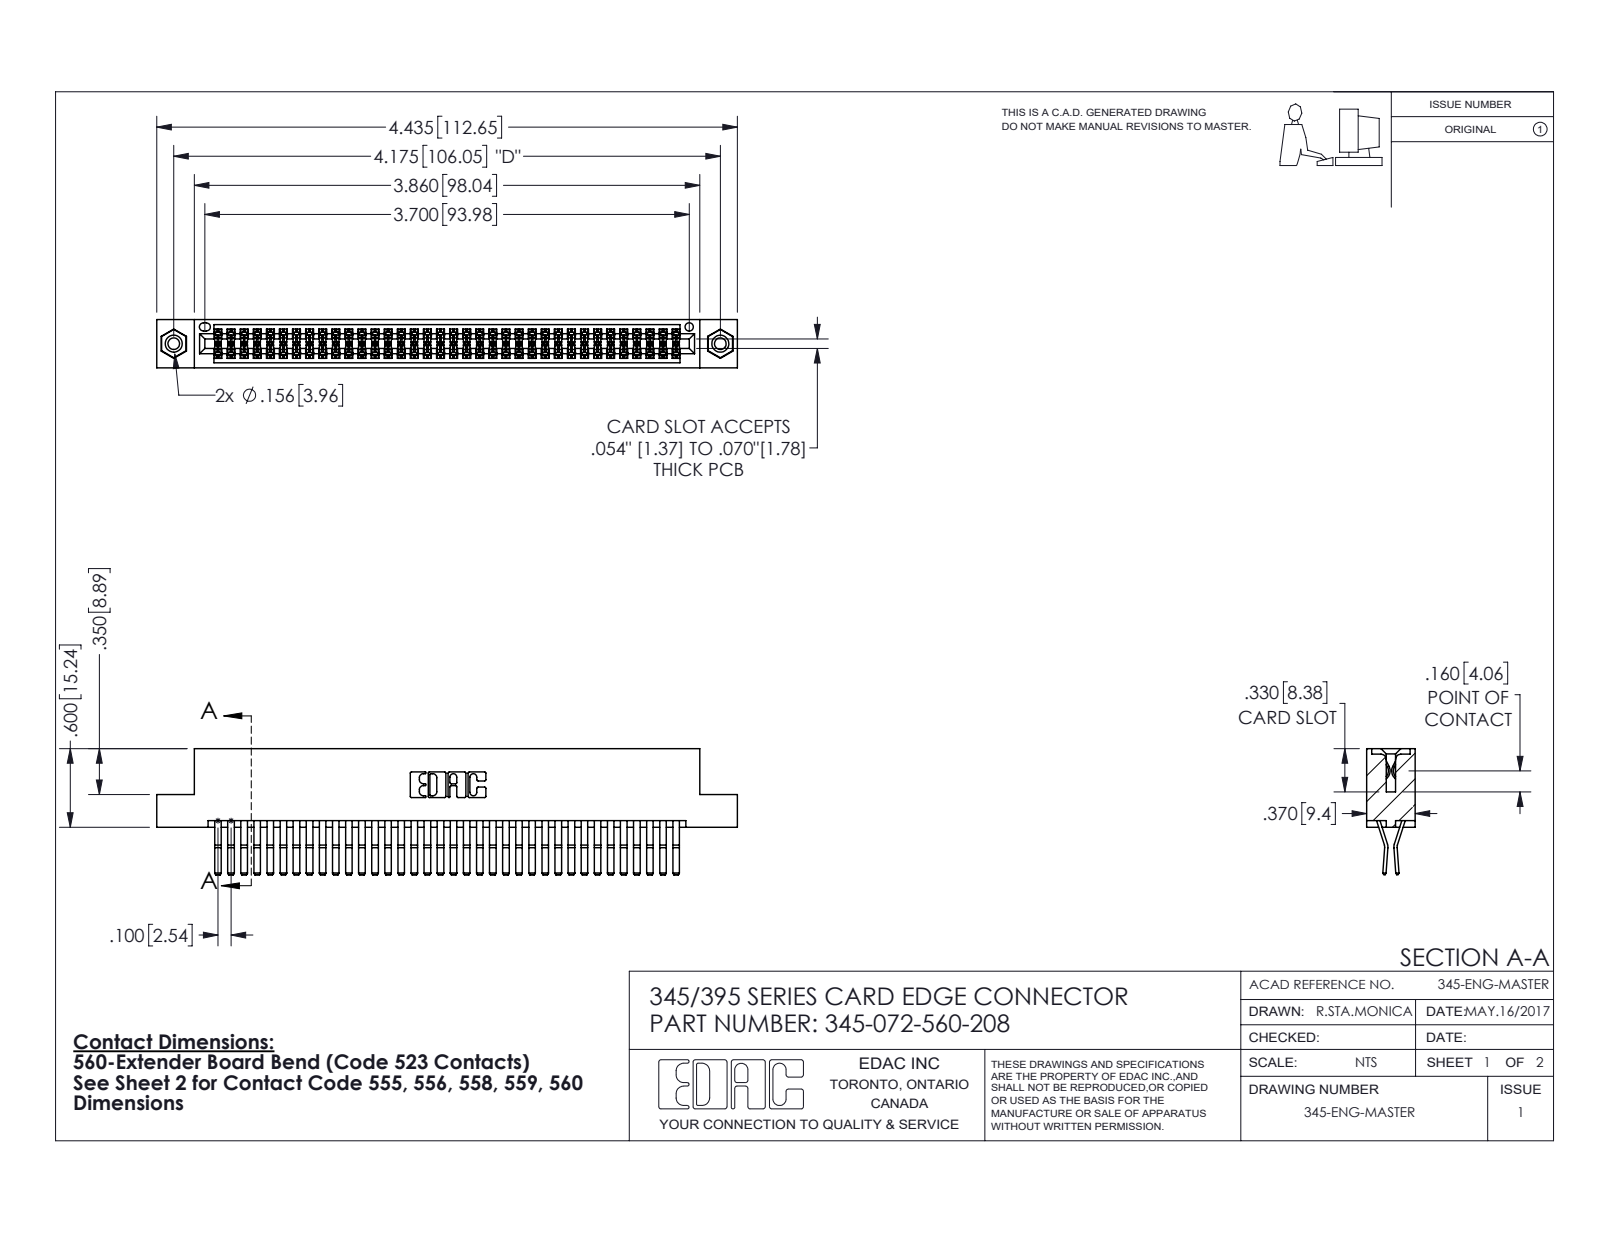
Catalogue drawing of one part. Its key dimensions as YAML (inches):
part_name: "345 Part_Flush Mounting Lugs - 0.156 Dia-TI; 345-292-001_560 Tail; 345-072-560-208; 345-250-001_345-250-003-102"
step_written_by: "SolidWorks 2016 (CONFIG_CONTROL_DESIGN)"
units: inches
bodies: {solids: 75, faces: 3930, planar: 2488, cylindrical: 1426, other: 16}
overall_size: [4.435, 0.962, 0.37]
volume: 0.693
surface_area: 27.73
round_holes:
  - {diameter: 0.089, count: 2}
  - {diameter: 0.125, count: 2}
  - {diameter: 0.156, count: 2}
  - {diameter: 0.064, count: 1}
round_bosses_or_shafts:
  - {diameter: 0.155, count: 2}
partial_cylinders:
  - {radius: 0.006, count: 108}
  - {radius: 0.01, count: 22}
  - {radius: 0.007, count: 6}
  - {radius: 0.031, count: 6}
  - {radius: 0.026, count: 3}
  - {radius: 0.01, count: 2}
  - {radius: 0.014, count: 2}
  - {radius: 0.019, count: 2}
face_to_face_distances: [0.025, 0.072, 0.298, 0.37, 0.2, 0.098, 0.272, 0.225, 0.175, 0.149]
hole_center_spacings: [0.27, 3.939, 4.175]
